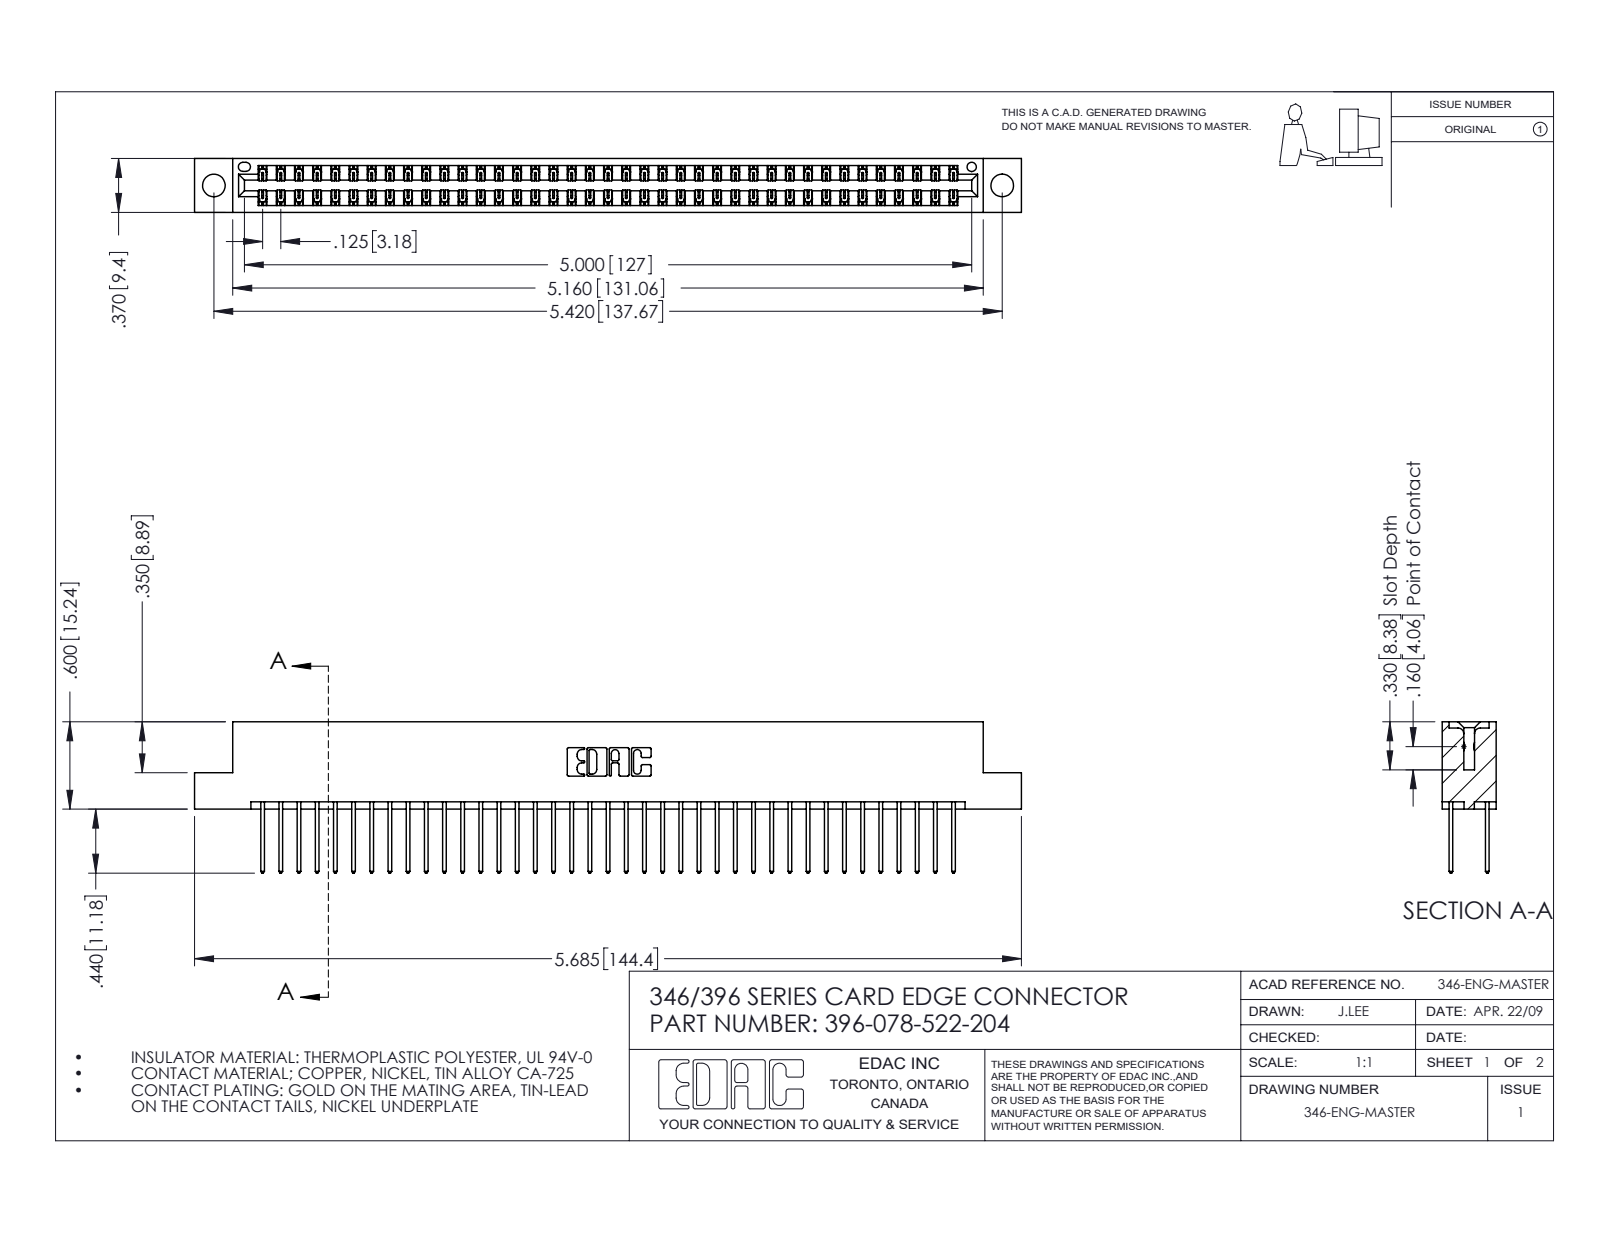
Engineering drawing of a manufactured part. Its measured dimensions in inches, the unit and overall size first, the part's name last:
Units: inches
Overall size (bounding box): 5.685 × 1.04 × 0.37
Round holes (diameter × count): ⌀0.156 ×2, ⌀0.064 ×1
Partial cylindrical surfaces — rounded edges, fillets, slot ends (radius × count): R0.006 ×117, R0.01 ×78, R0.01 ×22, R0.007 ×6, R0.031 ×6, R0.026 ×3, R0.014 ×2, R0.022 ×2
Main face-to-face distances: 0.048, 0.322, 0.25, 0.37, 0.072, 0.298, 0.025, 0.275, 0.148, 0.222
Hole centre spacings: 0.246, 5.211, 5.42
Volume: 0.865 in³ · Surface area: 31.26 in²
Bodies: 79 solids, 4178 faces (2806 planar, 1372 cylindrical, 0 other)
Part name (STEP PRODUCT): 396-078-522-204; 345-292-001_345-293-122; 346 Part_Flush Mounting Lugs - 0.156 Dia-TH
STEP written by: SolidWorks 2016 (CONFIG_CONTROL_DESIGN)
